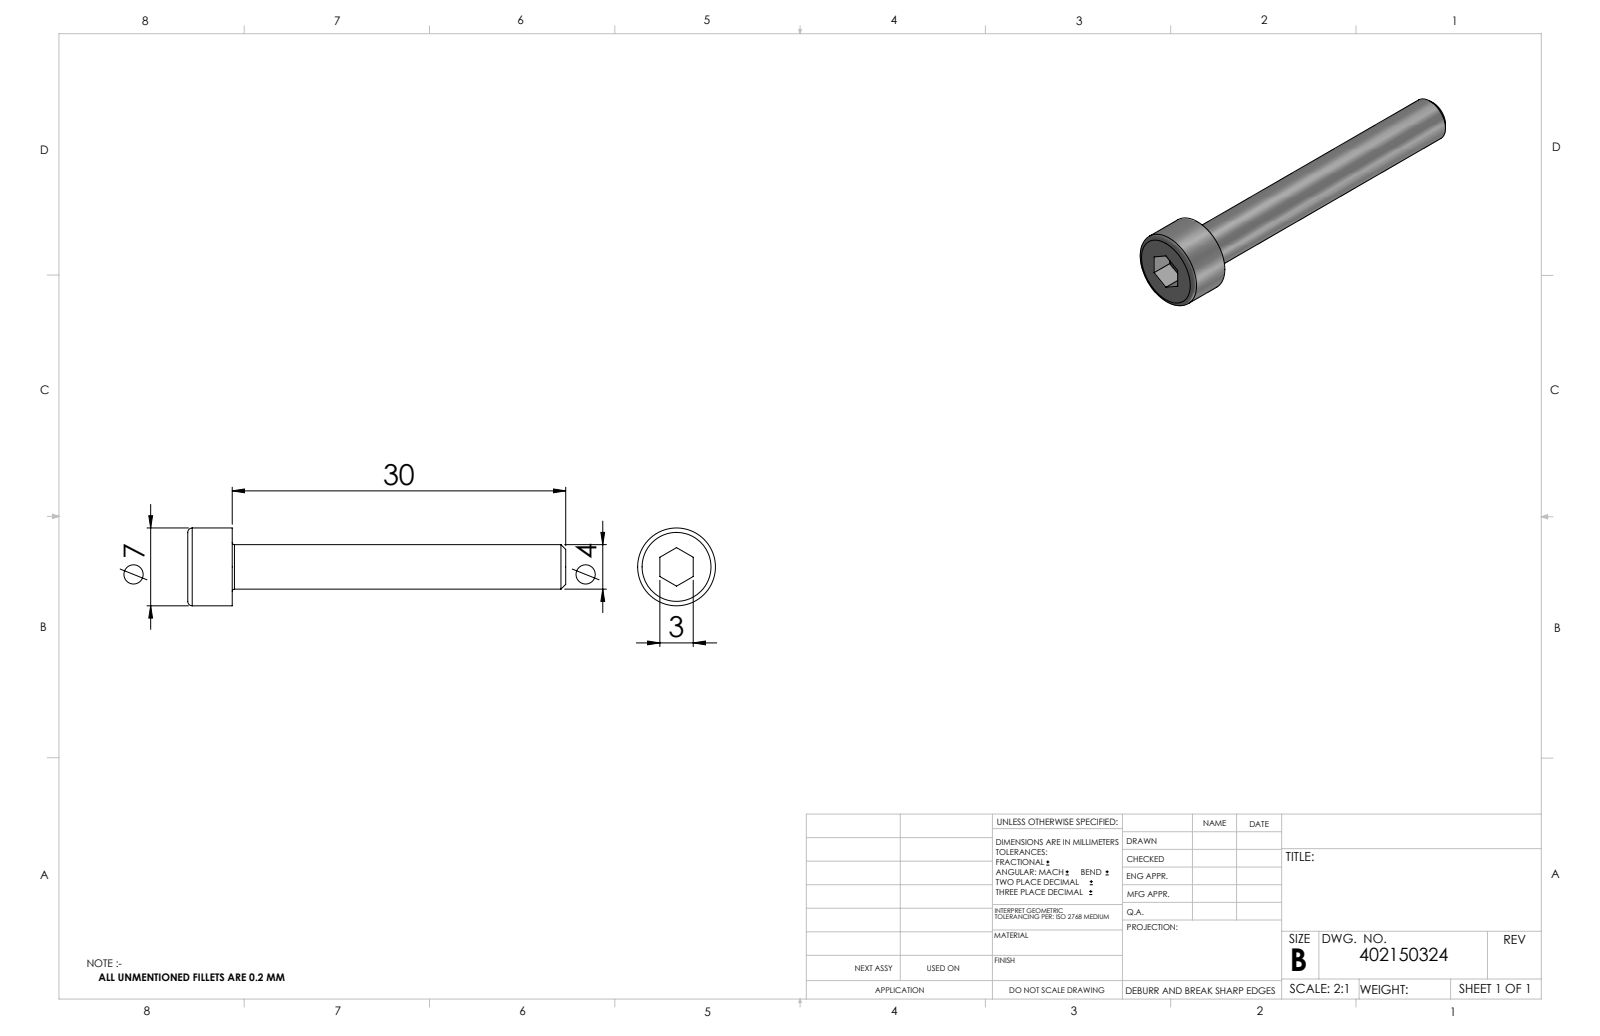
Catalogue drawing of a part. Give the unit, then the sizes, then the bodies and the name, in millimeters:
Units: millimetres
Overall size (bounding box): 34 × 7 × 7
Round bosses / shafts (diameter × count): ⌀7 ×1, ⌀4 ×1
Main face-to-face distances: 4, 2, 3, 34, 32, 30
Volume: 514 mm³ · Surface area: 554 mm²
Bodies: 1 solid, 20 faces (10 planar, 4 cylindrical, 6 other)
Part name (STEP PRODUCT): 402150324_c_1
STEP written by: SolidWorks 2014 (CONFIG_CONTROL_DESIGN)
